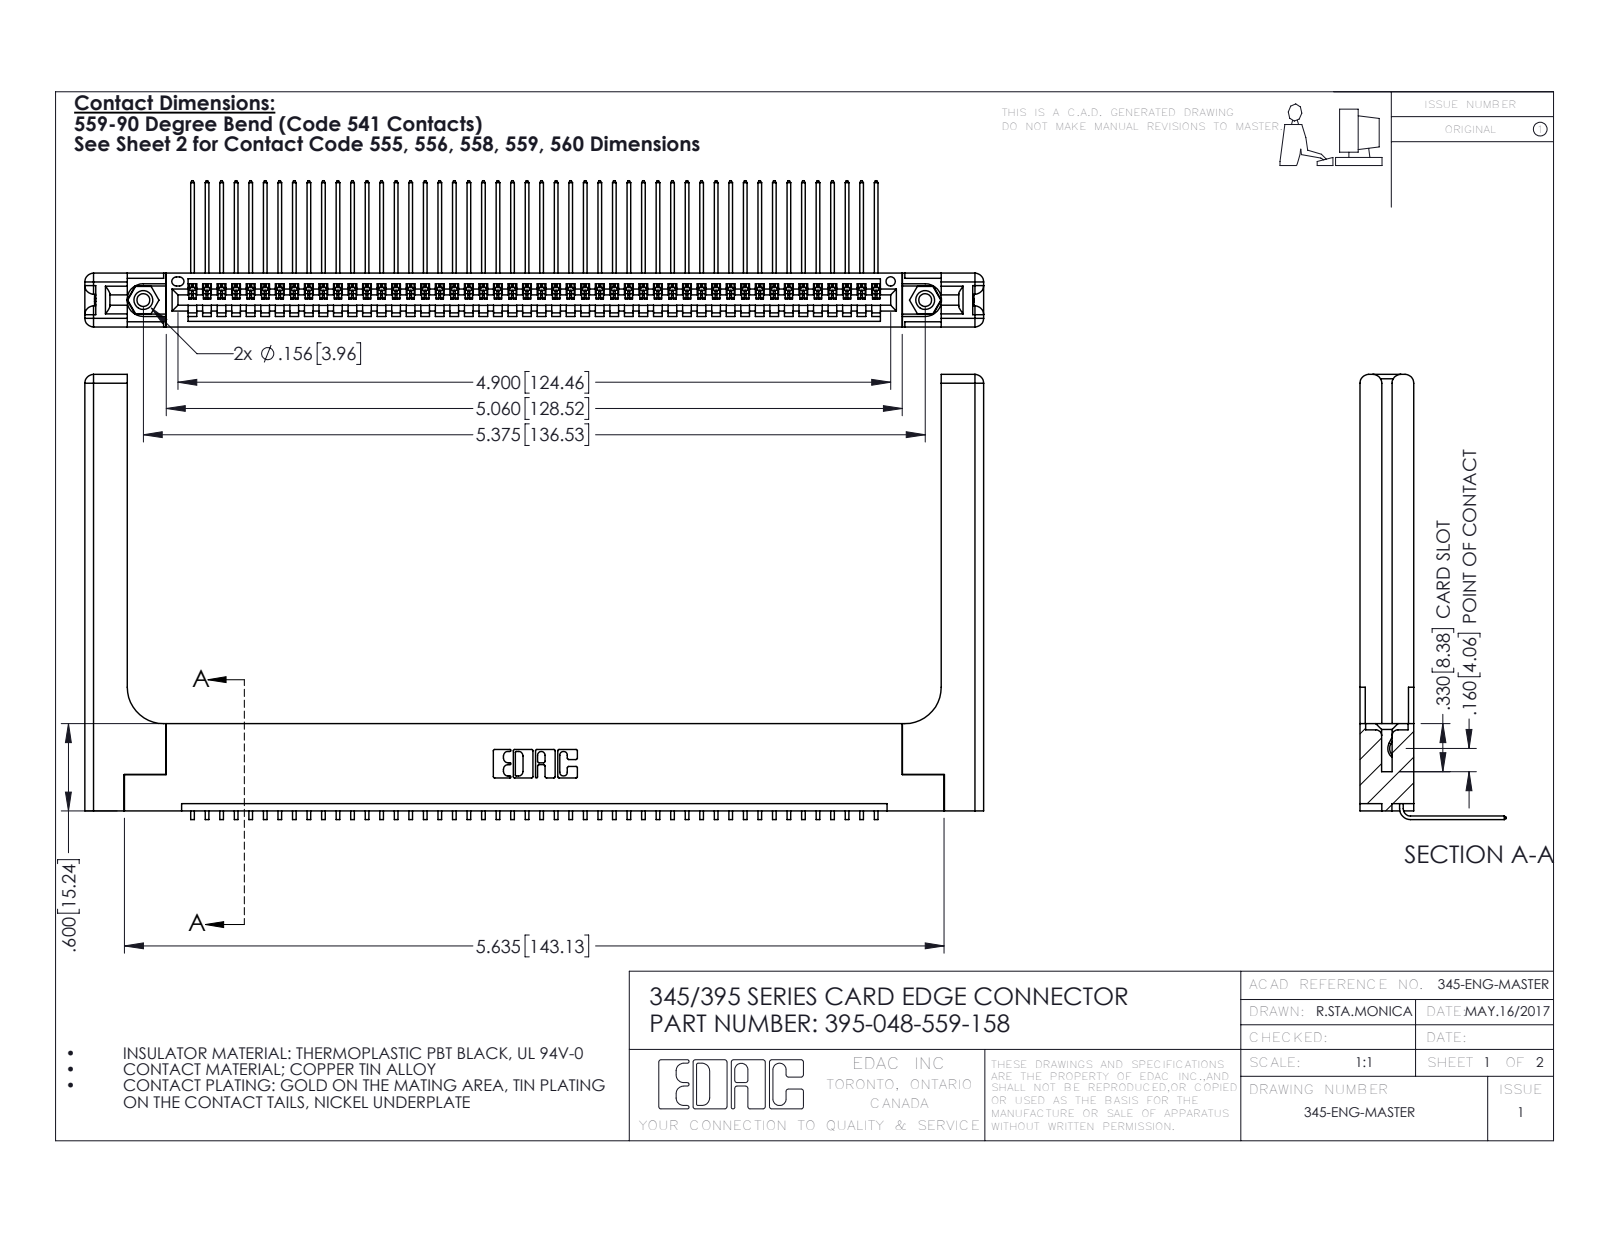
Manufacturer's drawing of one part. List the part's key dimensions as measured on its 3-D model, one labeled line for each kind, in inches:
Part name (STEP PRODUCT): 395-048-559-158; 345-220-058_345-220-058; 345 Part_Flush Mounting Lugs - 0.156 Dia-TH; 345-292-001_558 559 Tail - 1 (+1 more)
STEP written by: SolidWorks 2016 (CONFIG_CONTROL_DESIGN)
Units: inches
Bodies: 53 solids, 3262 faces (2244 planar, 958 cylindrical, 60 other)
Overall size (bounding box): 6.179 × 3.059 × 1.005
Volume: 1.441 in³ · Surface area: 40.94 in²
Round holes (diameter × count): ⌀0.089 ×2, ⌀0.125 ×2, ⌀0.156 ×2, ⌀0.064 ×1
Round bosses / shafts (diameter × count): ⌀0.155 ×2
Partial cylindrical surfaces — rounded edges, fillets, slot ends (radius × count): R0.006 ×96, R0.01 ×22, R0.06 ×16, R0.007 ×6, R0.031 ×6, R0.026 ×3, R0.03 ×2, R0.031 ×2
Main face-to-face distances: 0.37, 0.072, 0.298, 0.2, 0.098, 0.272, 0.025, 0.225, 0.148, 0.15
Hole centre spacings: 0.27, 5.139, 5.375
